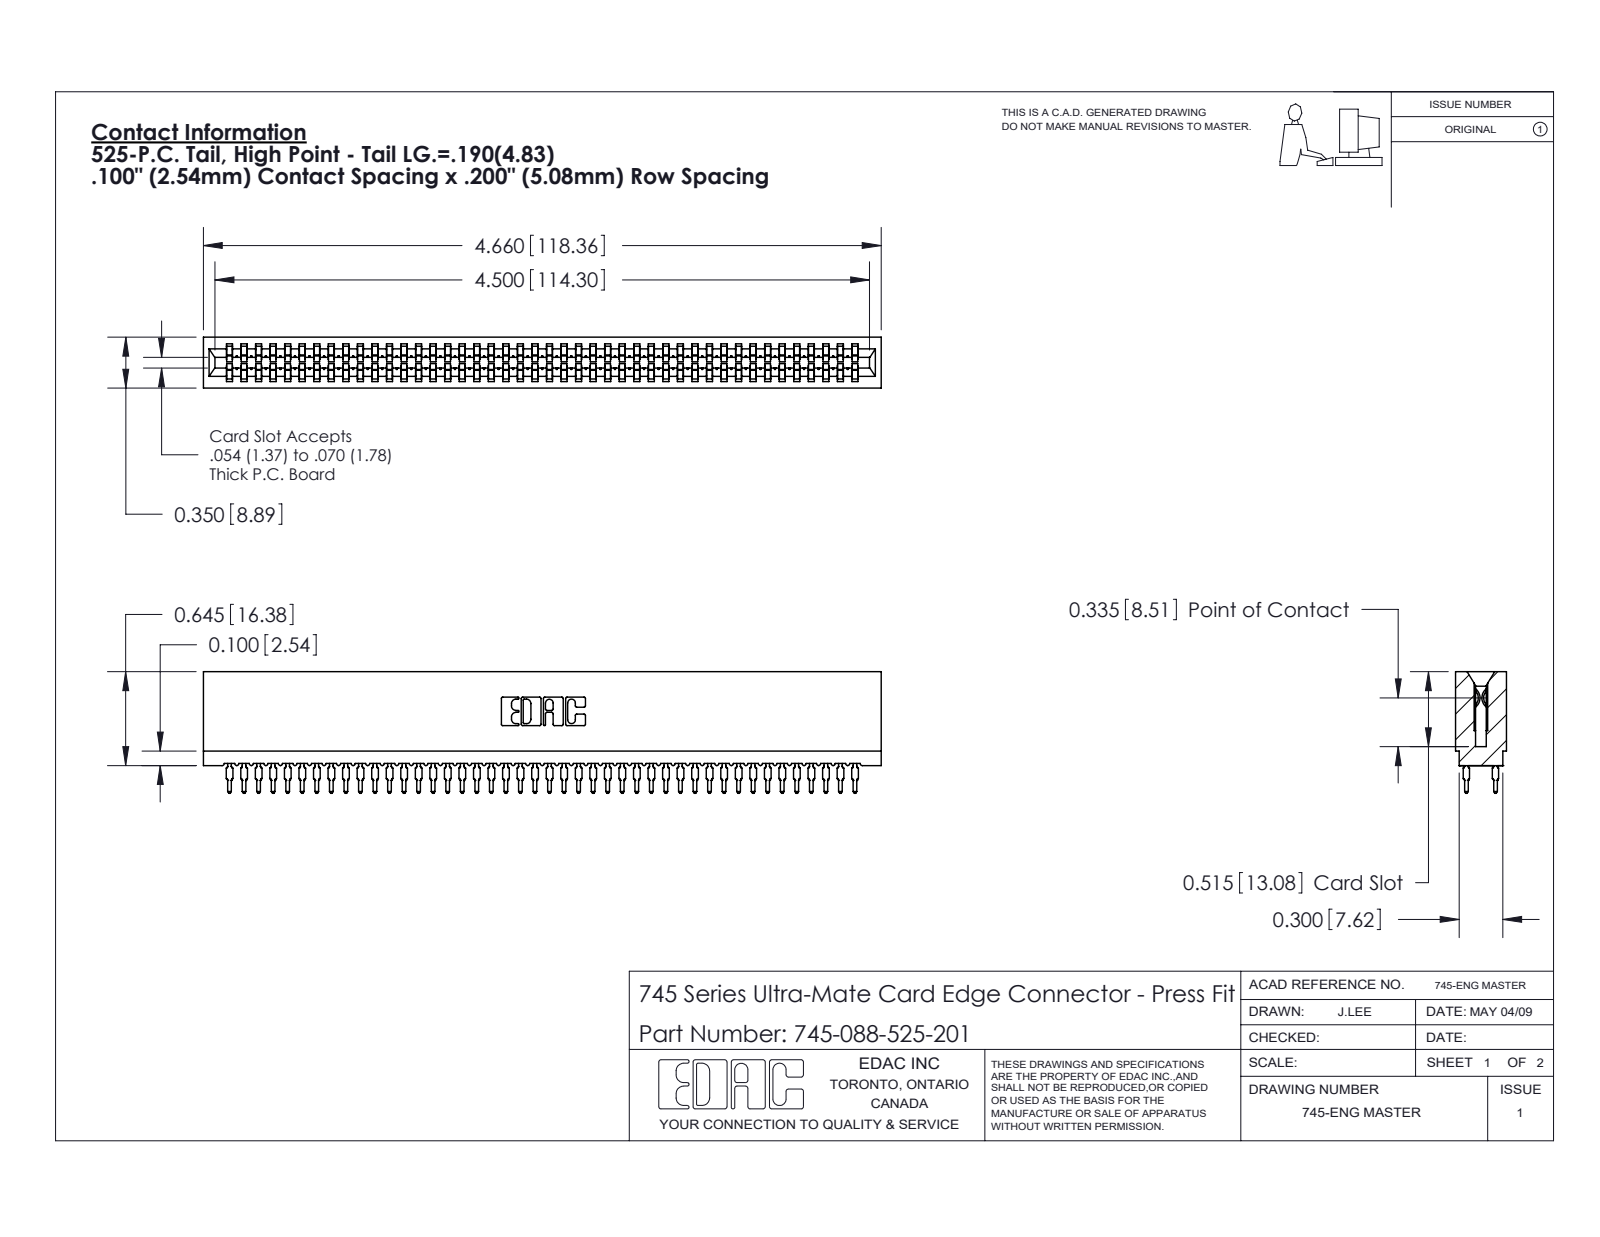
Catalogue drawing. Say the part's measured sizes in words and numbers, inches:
The part is named "745-088-525-201; 745 Part_Insulator Option - 01; 745-292-001_525". Its 3-D file was written by "SolidWorks 2020 (CONFIG_CONTROL_DESIGN)". It is 89 solids with 7971 faces: 4103 planar, 1580 cylindrical and 2288 other. Overall it measures 4.66 by 0.836 by 0.35 inches. Its volume is 0.648 cubic inches and its surface area 33.42 square inches. Partial cylindrical surfaces (rounded edges, fillets, slot ends): 176 of radius 0.021, 88 of radius 0.015, 22 of radius 0.01, 8 of radius 0.005, 8 of radius 0.011, 6 of radius 0.007, 6 of radius 0.031, 3 of radius 0.026. The main face-to-face distances are 0.35, 0.063, 0.287, 0.045, 0.305, 0.018, 0.243, 0.138, 0.212, 0.093.
